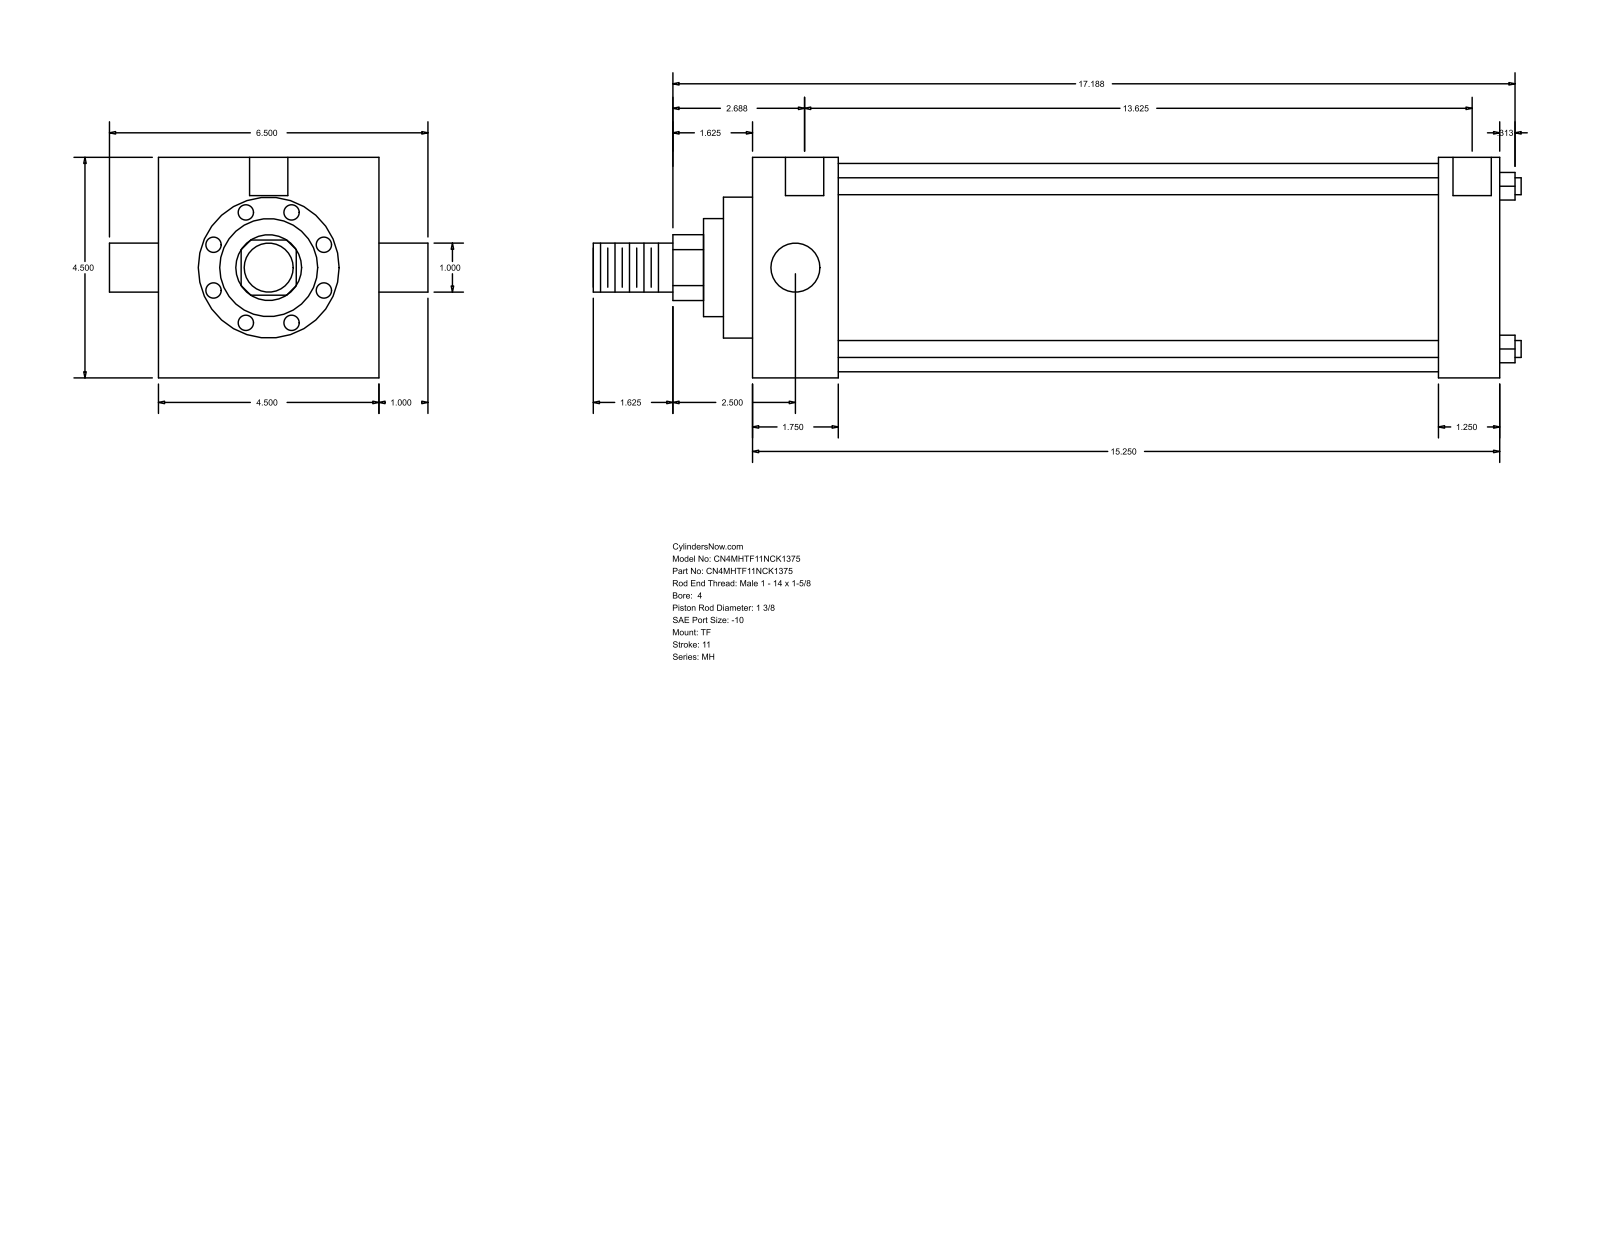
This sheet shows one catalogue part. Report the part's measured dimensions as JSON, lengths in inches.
{"part_name": "MH_TF__0400_1.375", "step_written_by": "GSSL Pune (CONFIG_CONTROL_DESIGN)", "units": "inches", "bodies": {"solids": 0, "faces": 86, "planar": 61, "cylindrical": 25, "other": 0}, "overall_size": [18.937, 6.5, 4.5], "round_holes": [[0.344, 3], [0.781, 2]], "round_bosses_or_shafts": [[0.345, 4], [1, 2], [4.25, 1], [2.875, 1], [2, 1], [1.375, 1]], "partial_cylinders_radius": [[0.672, 1]], "face_to_face_distances": [4.5, 15.25, 1.75, 13.5, 14, 12.25, 1.25, 0.594, 2.344, 14.594], "hole_center_spacings": [0.063, 13.688, 13.625, 13.75]}
